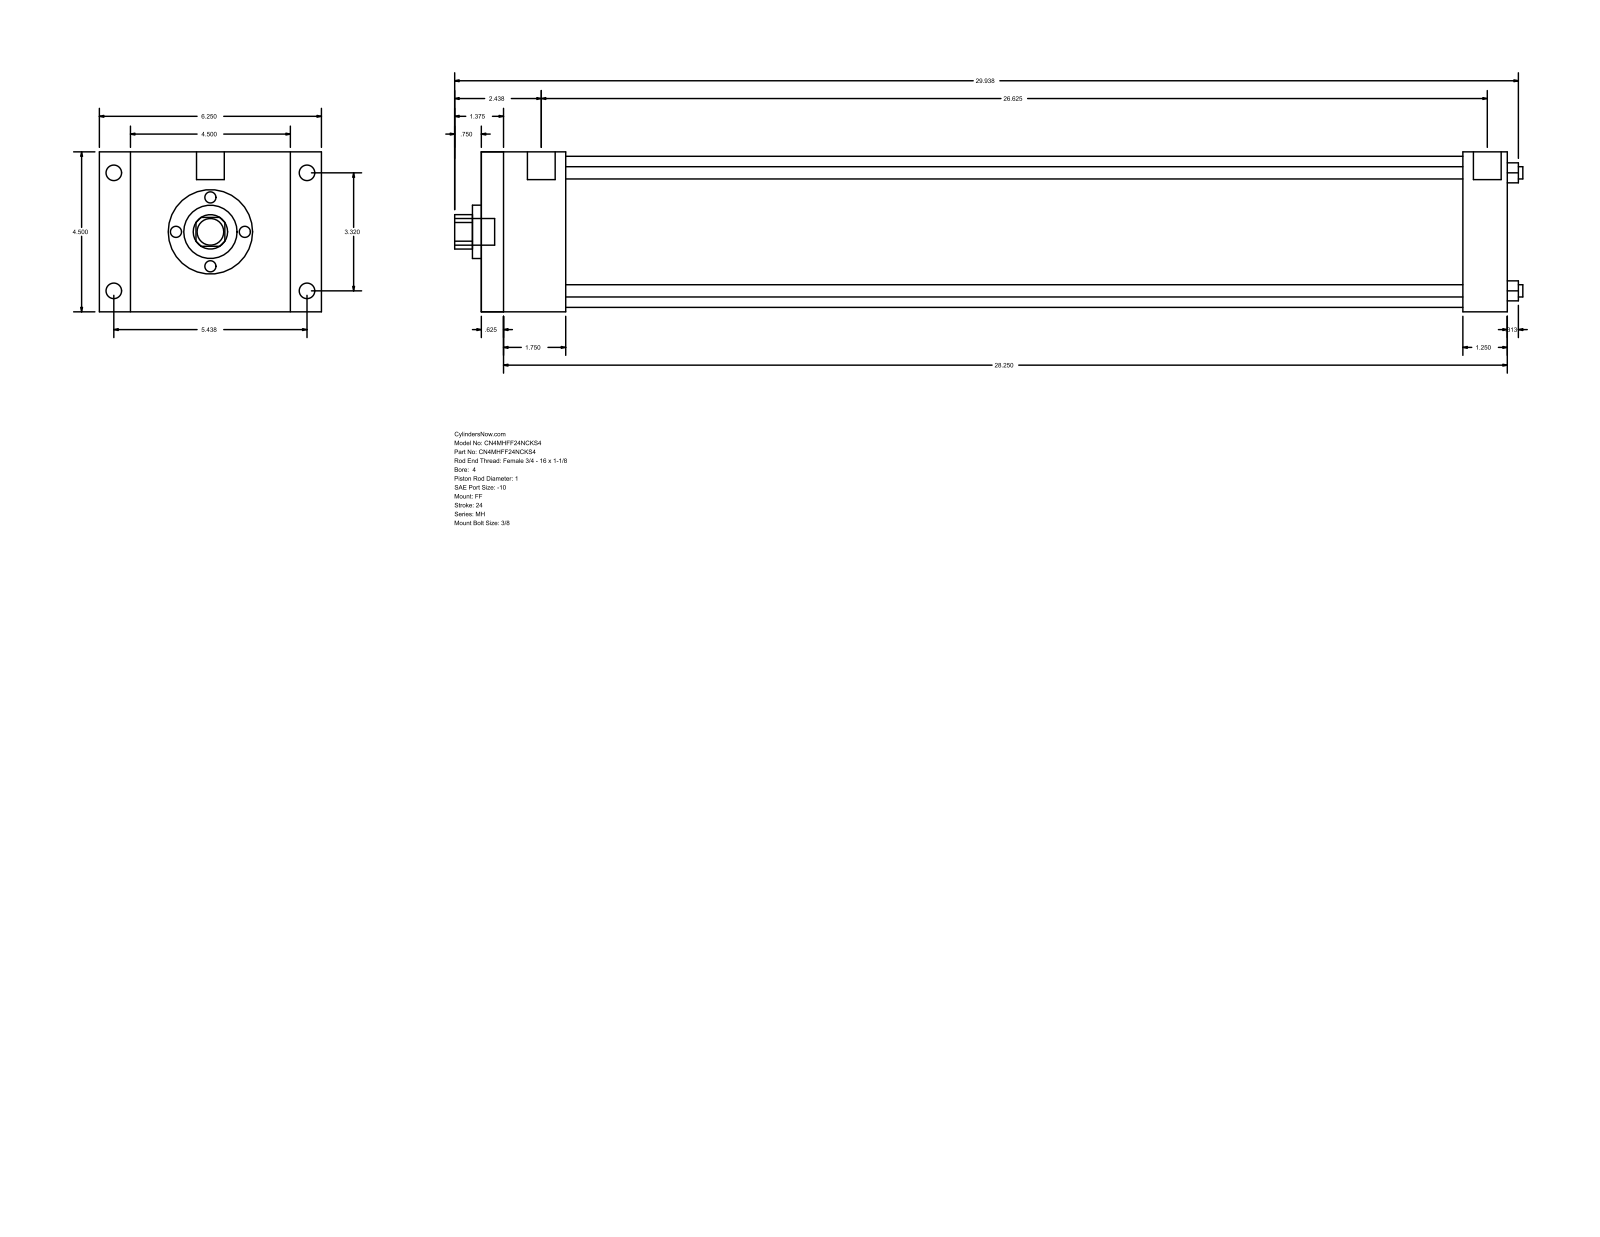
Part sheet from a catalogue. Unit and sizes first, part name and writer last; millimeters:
Units: millimetres
Overall size (bounding box): 763.59 × 158.75 × 114.3
Round holes (diameter × count): ⌀8.76 ×4, ⌀25.4 ×1, ⌀38.1 ×1, ⌀107.95 ×1
Round bosses / shafts (diameter × count): ⌀11.13 ×4, ⌀8.73 ×4, ⌀19.84 ×2, ⌀19.05 ×1
Partial cylindrical surfaces — rounded edges, fillets, slot ends (radius × count): R12.29 ×1
Main face-to-face distances: 114.3, 733.43, 15.87, 717.56, 60.33, 44.46, 673.1, 701.68, 685.81, 641.35
Hole centre spacings: 59.62, 84.32, 119.25
Bodies: 0 solids, 92 faces (64 planar, 28 cylindrical, 0 other)
Part name (STEP PRODUCT): MH_FF__0400_1
STEP written by: GSSL Pune (CONFIG_CONTROL_DESIGN)
